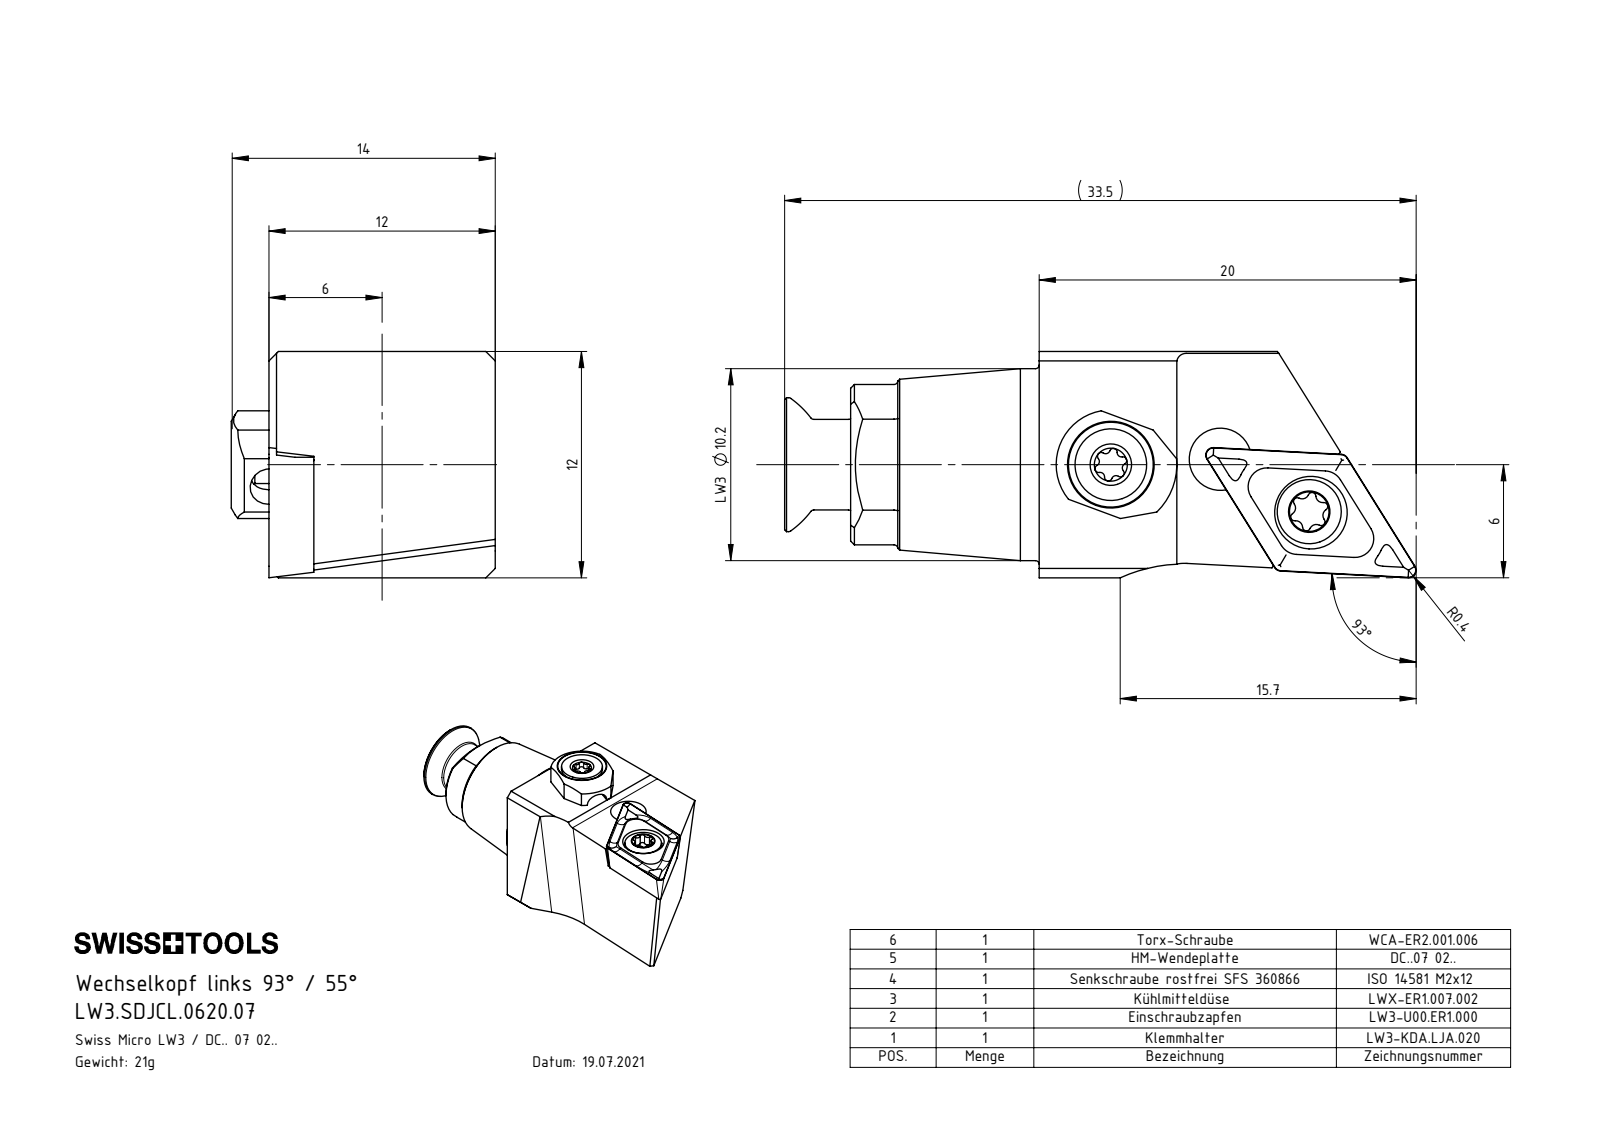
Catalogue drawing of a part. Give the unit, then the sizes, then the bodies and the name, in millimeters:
Units: millimetres
Overall size (bounding box): 33.39 × 14 × 12
Round holes (diameter × count): ⌀1.6 ×1, ⌀2 ×1, ⌀2.05 ×1, ⌀2.5 ×1, ⌀2.8 ×1, ⌀3 ×1, ⌀3.3 ×1, ⌀3.85 ×1, ⌀5.5 ×1
Round bosses / shafts (diameter × count): ⌀10.18 ×1, ⌀6.9 ×1, ⌀6 ×1, ⌀5 ×1, ⌀4.8 ×1, ⌀3.8 ×1, ⌀3.4 ×1, ⌀2.5 ×1
Partial cylindrical surfaces — rounded edges, fillets, slot ends (radius × count): R0.2 ×8, R0.21 ×6, R0.24 ×6, R0.36 ×4, R0.36 ×2, R0.5 ×1, R1 ×1, R2.9 ×1
Main face-to-face distances: 12, 9.62, 2.38, 11.6, 1.98, 0.4, 2, 2.5, 13.4, 11.4
Hole centre spacings: 5.47, 5.57, 5.82, 10.81, 10.91
Volume: 2 686 mm³ · Surface area: 2 306 mm²
Bodies: 6 solids, 252 faces (70 planar, 78 cylindrical, 104 other)
Part name (STEP PRODUCT): LW3-U00.ER1.000_B; ISO 14581 - M2x12; DCMT070204; LWX-ER1.007.002 (+3 more)
STEP written by: SolidWorks 2022 (CONFIG_CONTROL_DESIGN)
